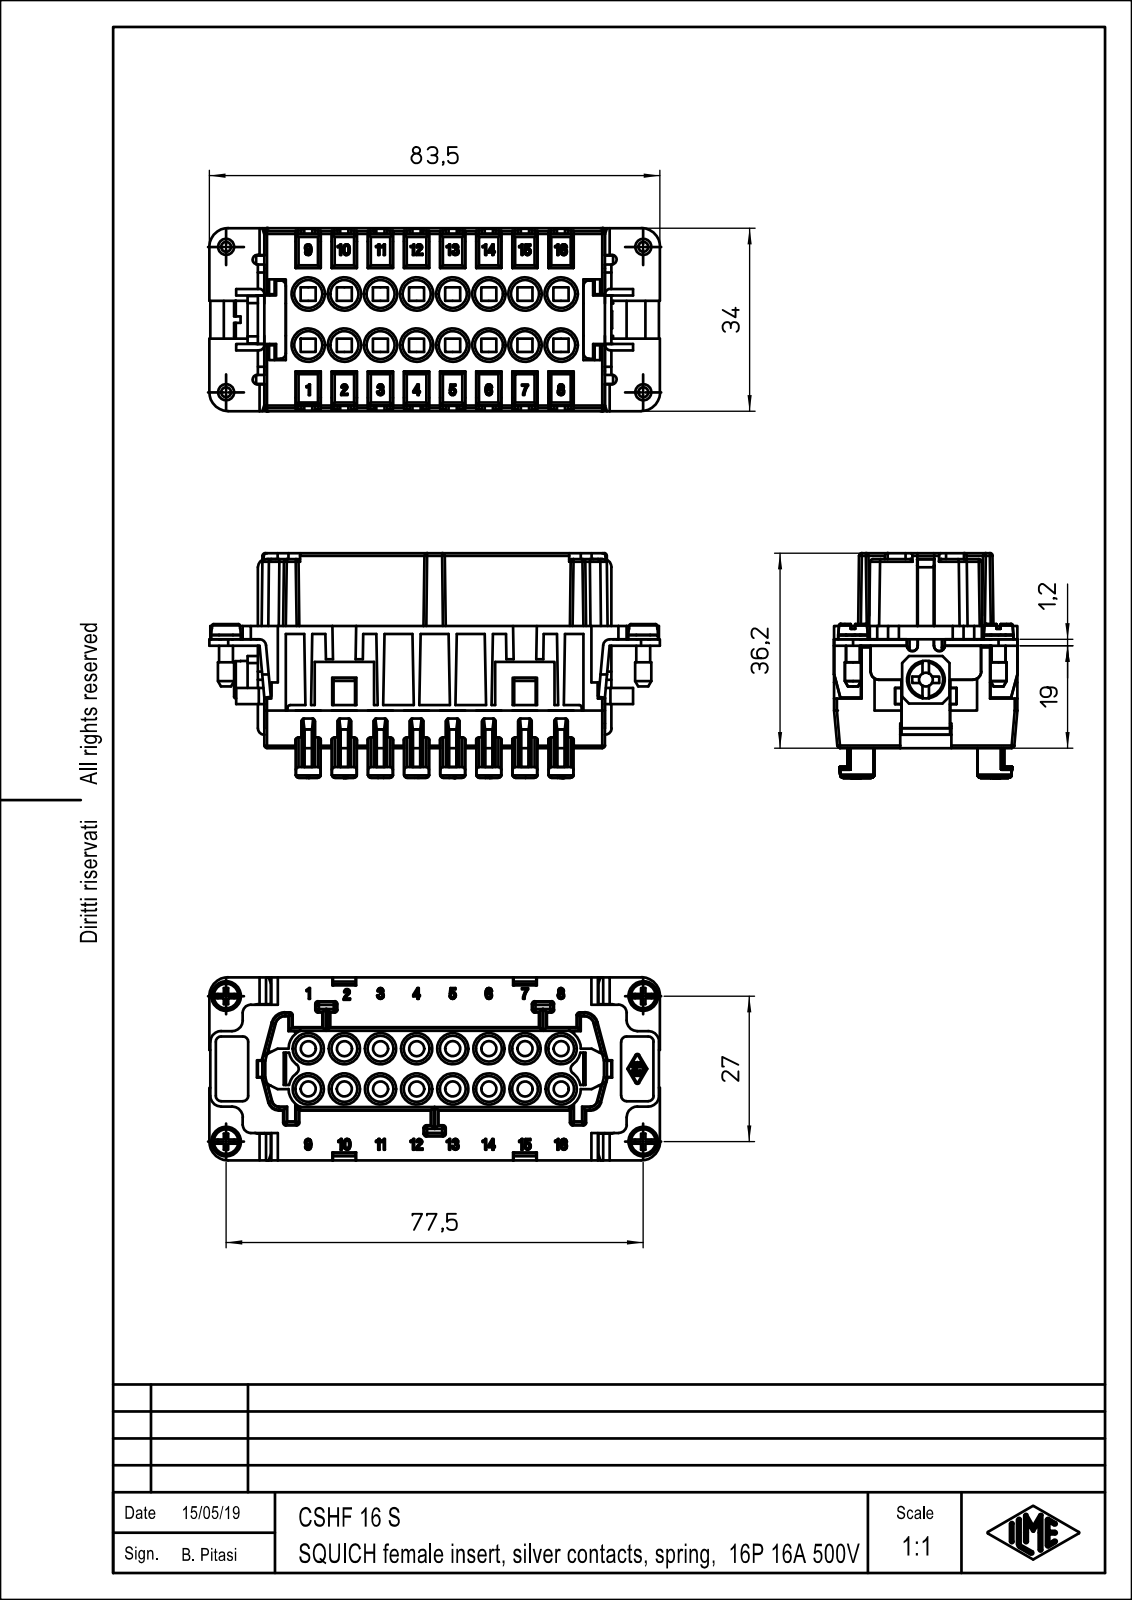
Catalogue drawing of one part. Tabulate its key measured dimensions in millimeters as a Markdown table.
| quantity | value |
| --- | --- |
| part name | CSHF_16_S |
| STEP written by | Creo Elements/Direct Modeling 20.1B 02-Apr-2019 (C) Parametric Technology GmbH (AUTOMOTIVE_DESIGN) |
| units | millimeters |
| bodies | 1 solid, 2061 faces (1283 planar, 620 cylindrical, 158 other) |
| overall size | 83.6 × 41.7 × 34 |
| volume | 55 608 mm³ |
| surface area | 29 523 mm² |
| round holes (diameter × count) | 2.8 × 20, 5.2 × 16, 5.8 × 16, 2.58 × 1, 4.2 × 1 |
| round bosses / shafts (diameter × count) | 5.5 × 4, 3 × 4, 2.6 × 4, 7 × 1, 6 × 1, 4 × 1 |
| partial cylindrical surfaces (radius × count) | 0.5 × 171, 0.3 × 40, 1 × 22, 1.15 × 16, 1.5 × 10, 2 × 10, 1.2 × 6, 0.88 × 4 |
| main face-to-face distances | 1.5, 6.7, 1.2, 13.4, 12.5, 20.1, 32.5, 2.5, 22.7, 19 |
| hole center spacings | 6.7, 6.77, 10.82, 13.4, 13.44, 15.87, 20.1, 20.12 |
